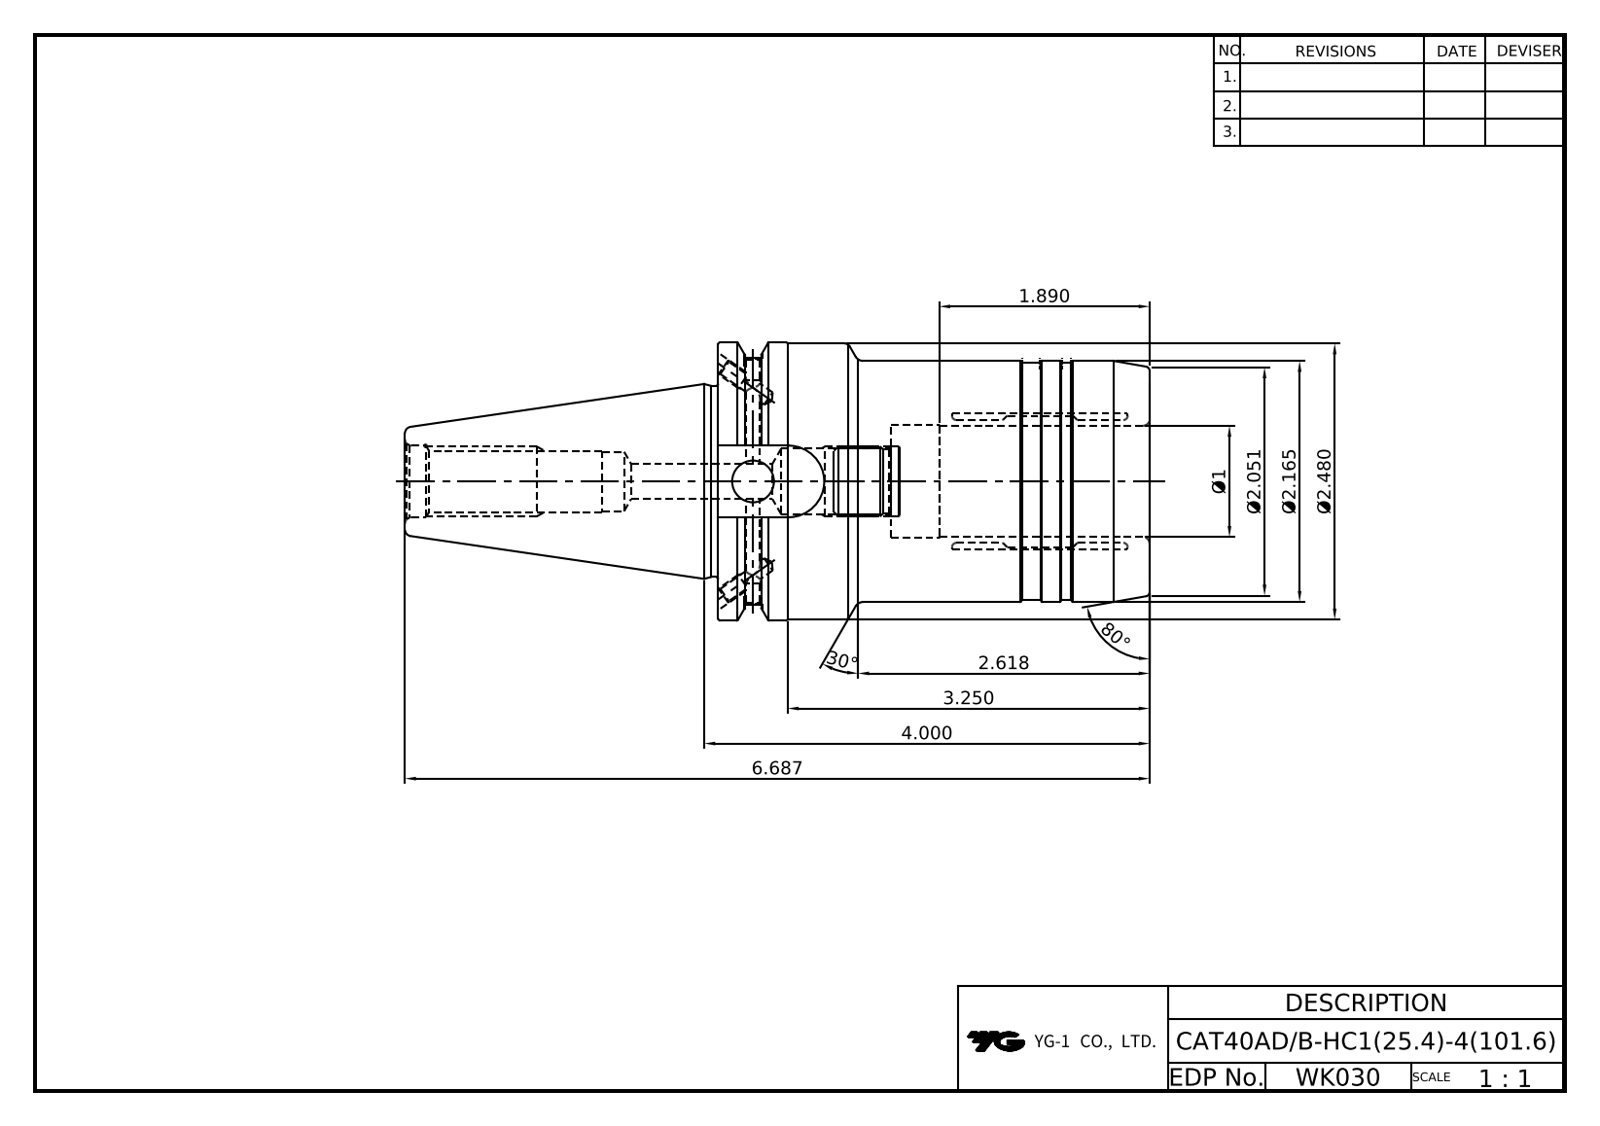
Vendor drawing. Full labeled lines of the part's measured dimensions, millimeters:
Part name (STEP PRODUCT): WK030
STEP written by: CREO PARAMETRIC BY PTC INC, 2018100 (CONFIG_CONTROL_DESIGN)
Units: millimetres
Bodies: 1 solid, 205 faces (55 planar, 76 cylindrical, 74 other)
Overall size (bounding box): 169.85 × 63.5 × 63
Volume: 270 679 mm³ · Surface area: 44 240 mm²
Round holes (diameter × count): ⌀3.3 ×3, ⌀4 ×3, ⌀4.2 ×1, ⌀8 ×1, ⌀9.53 ×1, ⌀11 ×1, ⌀14 ×1, ⌀15.1 ×1, ⌀15.88 ×1, ⌀16 ×1, ⌀16.3 ×1, ⌀25.4 ×1
Round bosses / shafts (diameter × count): ⌀63.5 ×1, ⌀63 ×1, ⌀55 ×1, ⌀54 ×1, ⌀43.6 ×1
Partial cylindrical surfaces — rounded edges, fillets, slot ends (radius × count): R8.19 ×1, R28.15 ×1
Main face-to-face distances: 98.43, 39.43, 59, 47.6, 16.38, 71.42, 110.85, 169.85, 77.47, 6.05
